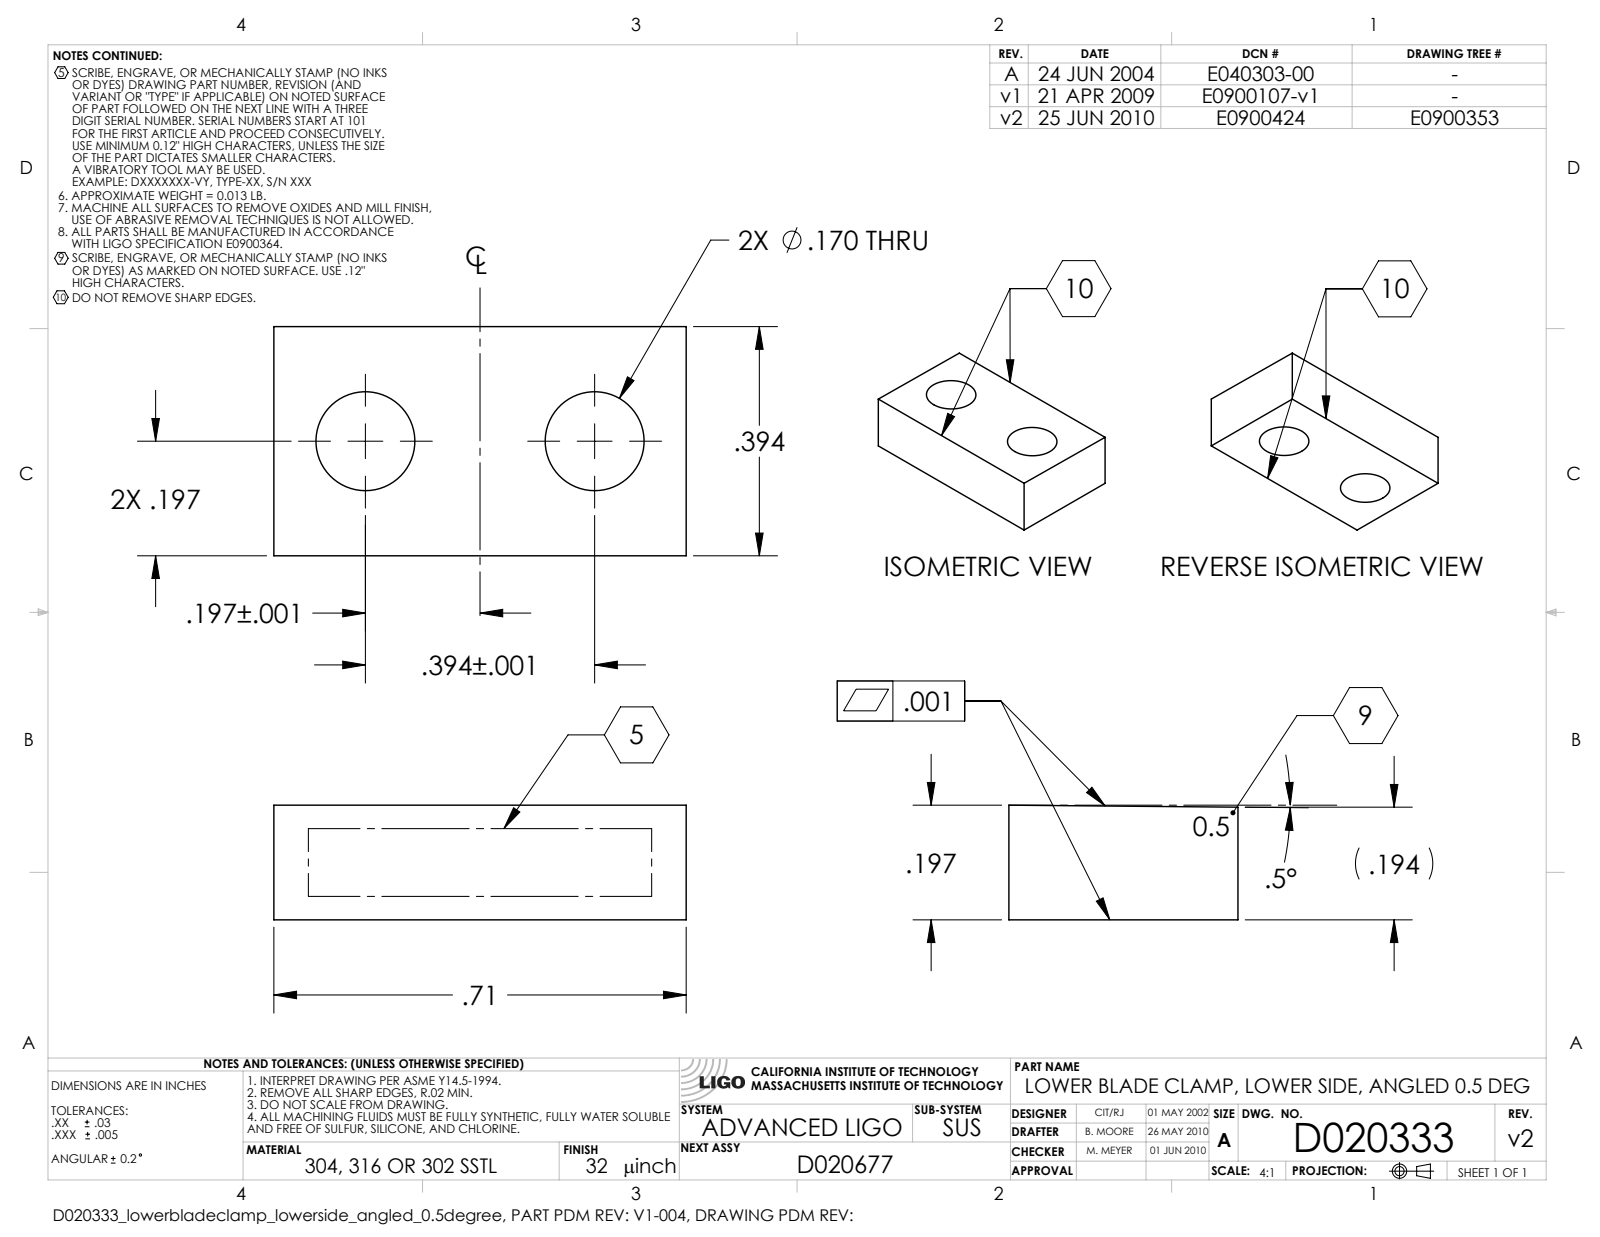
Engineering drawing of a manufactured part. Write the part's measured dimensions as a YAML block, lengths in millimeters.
part_name: "D020333-v2_aLIGO_SUS_HSTS_Lower Blade Clamp, Lower Side, Angled 0.5"
step_written_by: "SolidWorks 2009 (CONFIG_CONTROL_DESIGN)"
units: millimeters
bodies: {solids: 1, faces: 10, planar: 6, cylindrical: 4, other: 0}
overall_size: [18, 10, 5]
volume: 750
surface_area: 714
round_holes:
  - {diameter: 4.3, count: 2}
face_to_face_distances: [10, 18]
hole_center_spacings: [10]
